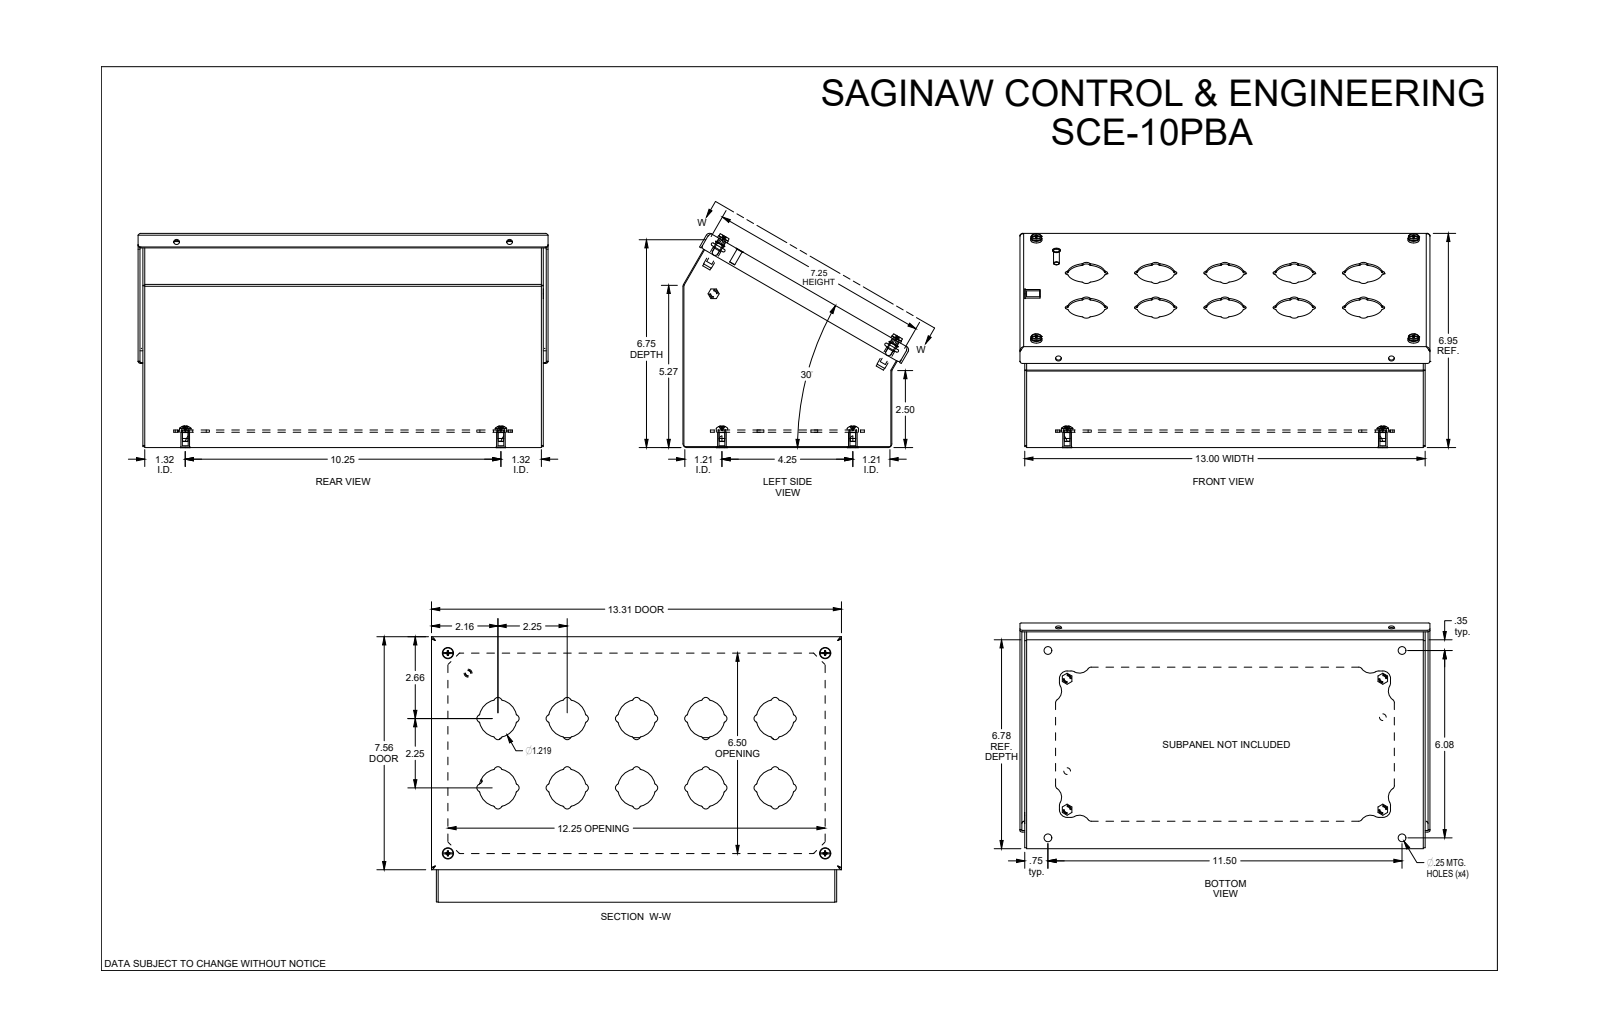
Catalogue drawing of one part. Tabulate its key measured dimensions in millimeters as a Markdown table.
| quantity | value |
| --- | --- |
| part name | SCE-10PBA |
| STEP written by | SolidWorks 2019 (AUTOMOTIVE_DESIGN) |
| units | millimeters |
| bodies | 20 solids, 727 faces (250 planar, 409 cylindrical, 68 other) |
| overall size | 338.2 × 186.6 × 177.2 |
| volume | 484 400 mm³ |
| surface area | 626 300 mm² |
| round holes (diameter × count) | 6.4 × 12, 4.8 × 9, 5.6 × 4, 6.8 × 4, 7.1 × 4, 8.1 × 4, 4.7 × 2, 5.5 × 2, 4.9 × 1 |
| round bosses / shafts (diameter × count) | 7.1 × 5, 9.2 × 4, 8.6 × 4, 7.4 × 4, 6.9 × 4, 6.6 × 4, 6.5 × 1, 4.8 × 1 |
| partial cylindrical surfaces (radius × count) | 1 × 84, 3.2 × 48, 1.5 × 20, 0.8 × 12, 6.4 × 12, 0.3 × 10, 15.5 × 10, 2.9 × 8 |
| main face-to-face distances | 1.5, 1.5, 328.7, 170.7, 12.6, 11.1, 1.9, 13, 14.5, 327.2 |
| hole center spacings | 165.1, 311.2, 165.2, 277.2, 305.8, 311.2, 352.2, 28.1 |
